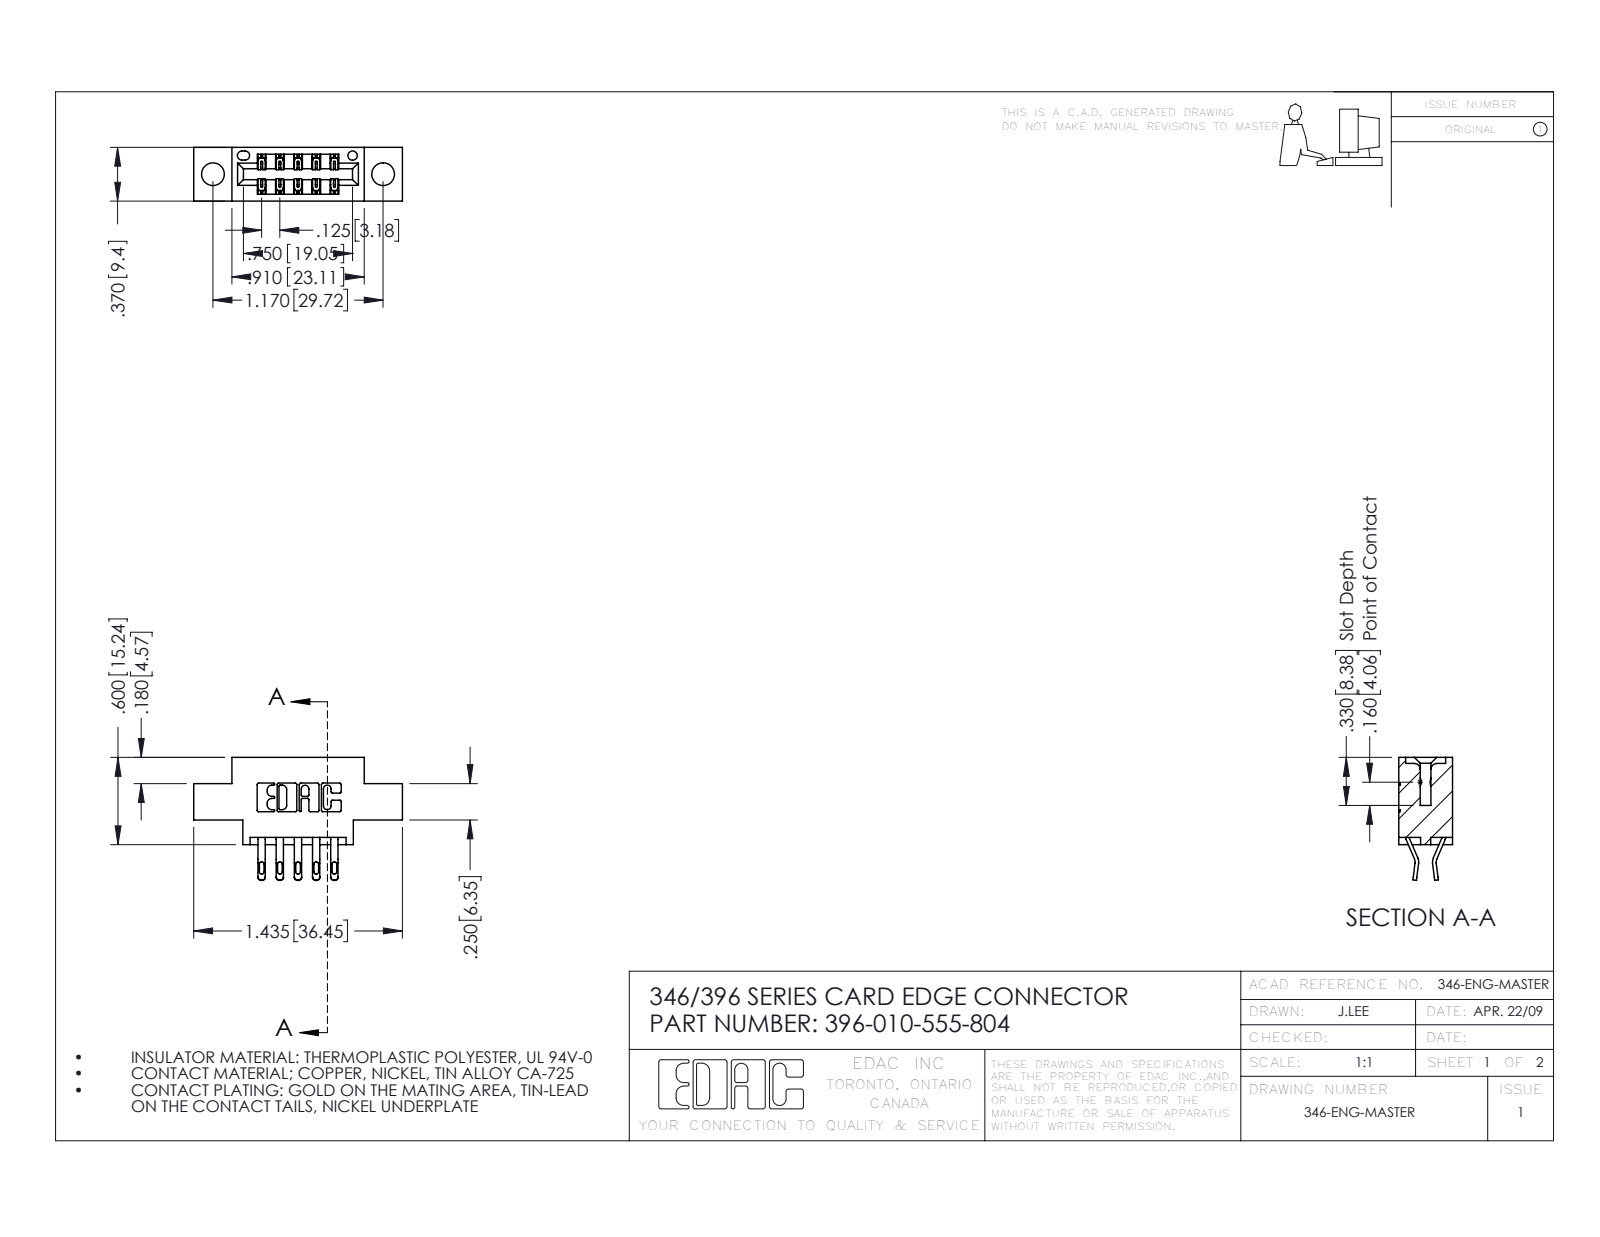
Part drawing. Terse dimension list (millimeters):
name: 345-292-001_555 Tail; 396-010-555-804; 346 Part_0.170 Offset - 0.156 Dia-TH
written by: SolidWorks 2016 (CONFIG_CONTROL_DESIGN)
unit: mm
bodies: 11 solids, 706 faces (410 planar, 296 cylindrical, 0 other)
size: 36.4 × 21.5 × 9.4
volume: 3 050 mm³; area: 3 712 mm²
holes: 2× ⌀4, 1× ⌀1.6
rounds: 22× R0.3, 20× R0.4, 20× R0.5, 15× R0.2, 6× R0.2, 6× R0.8, 3× R0.7, 2× R0.3
face distances: 9.4, 6.4, 1.2, 8.2, 3.2, 3.8, 5.6, 2.5, 4.4, 0.6
hole spacings: 6.2, 24.6, 29.7
